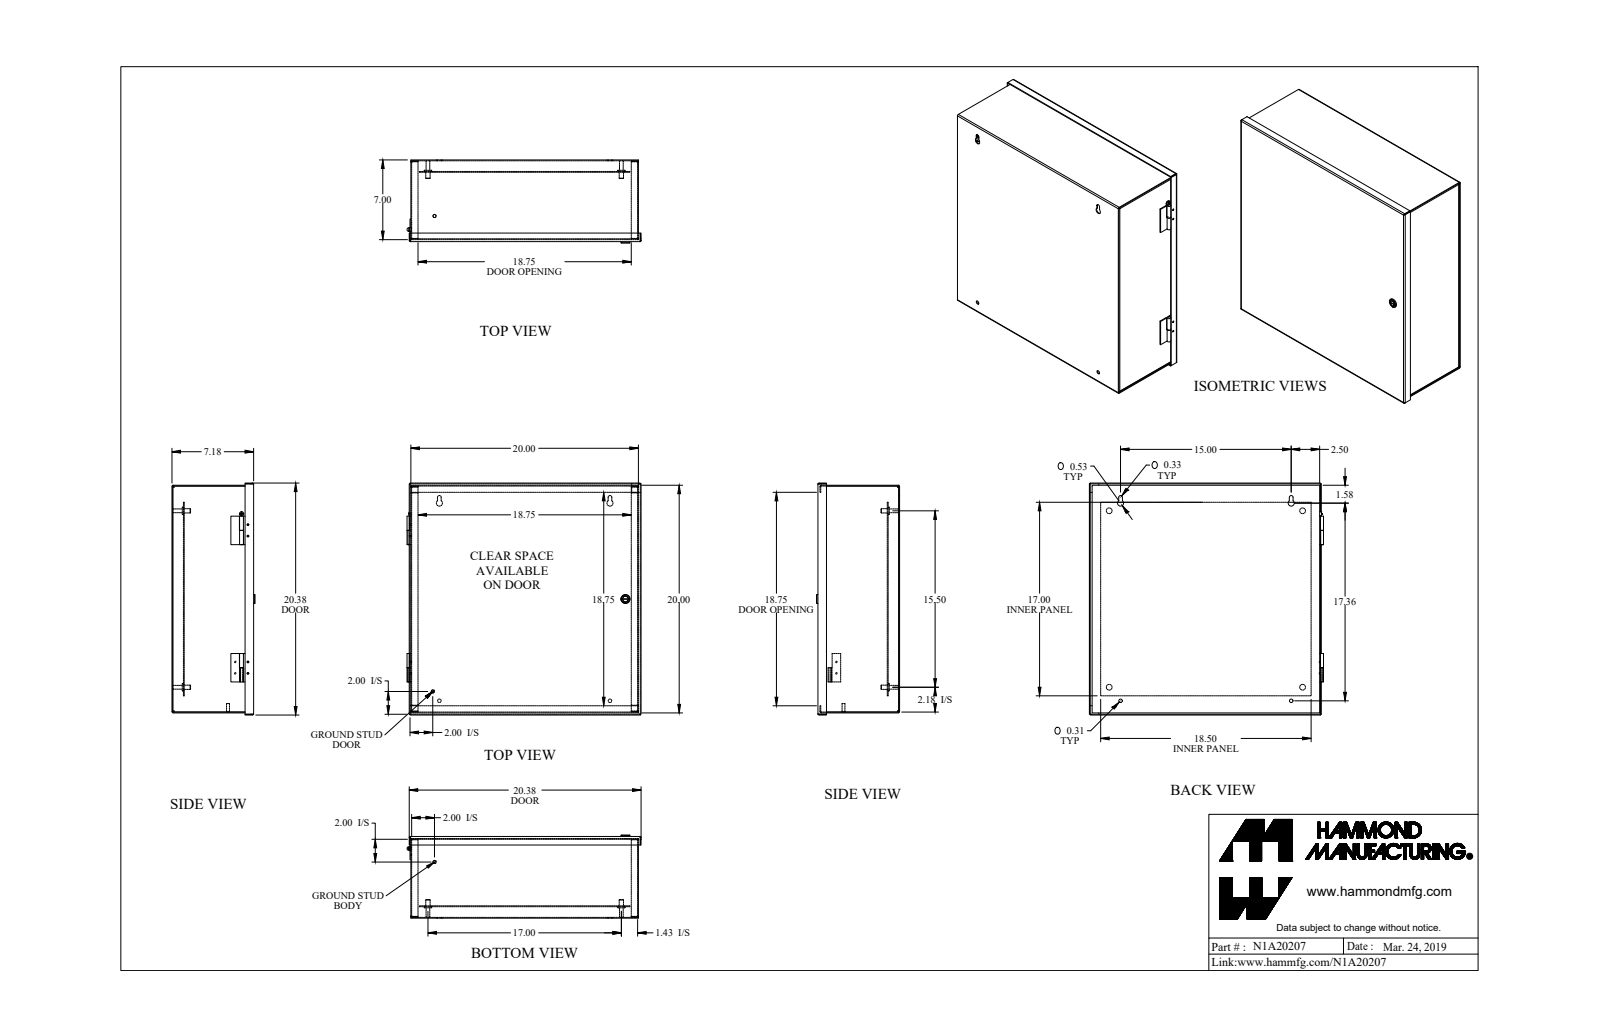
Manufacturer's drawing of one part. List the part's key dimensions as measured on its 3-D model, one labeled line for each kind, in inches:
Part name (STEP PRODUCT): N1A20207
STEP written by: SolidWorks 2018 (AUTOMOTIVE_DESIGN)
Units: inches
Bodies: 23 solids, 520 faces (294 planar, 182 cylindrical, 44 other)
Overall size (bounding box): 20.574 × 20.384 × 7.299
Volume: 132.5 in³ · Surface area: 3 692 in²
Round holes (diameter × count): ⌀0.14 ×8, ⌀0.5 ×4, ⌀0.307 ×2, ⌀0.312 ×2, ⌀0.445 ×2, ⌀0.17 ×1, ⌀0.187 ×1, ⌀0.516 ×1
Round bosses / shafts (diameter × count): ⌀0.128 ×8, ⌀0.375 ×5, ⌀0.65 ×4, ⌀0.33 ×4, ⌀1 ×2, ⌀0.281 ×2, ⌀0.25 ×2, ⌀0.788 ×1
Partial cylindrical surfaces — rounded edges, fillets, slot ends (radius × count): R0.036 ×16, R0.108 ×16, R0.06 ×2, R0.153 ×2, R0.164 ×2, R0.266 ×2, R0.03 ×1, R0.125 ×1
Main face-to-face distances: 0.072, 7.105, 1.009, 6.096, 19.928, 7.033, 7.177, 1.081, 6.024, 0.937
Hole centre spacings: 1, 1.119, 1.104, 1.553, 2.031, 7.758, 12.062, 12.062
